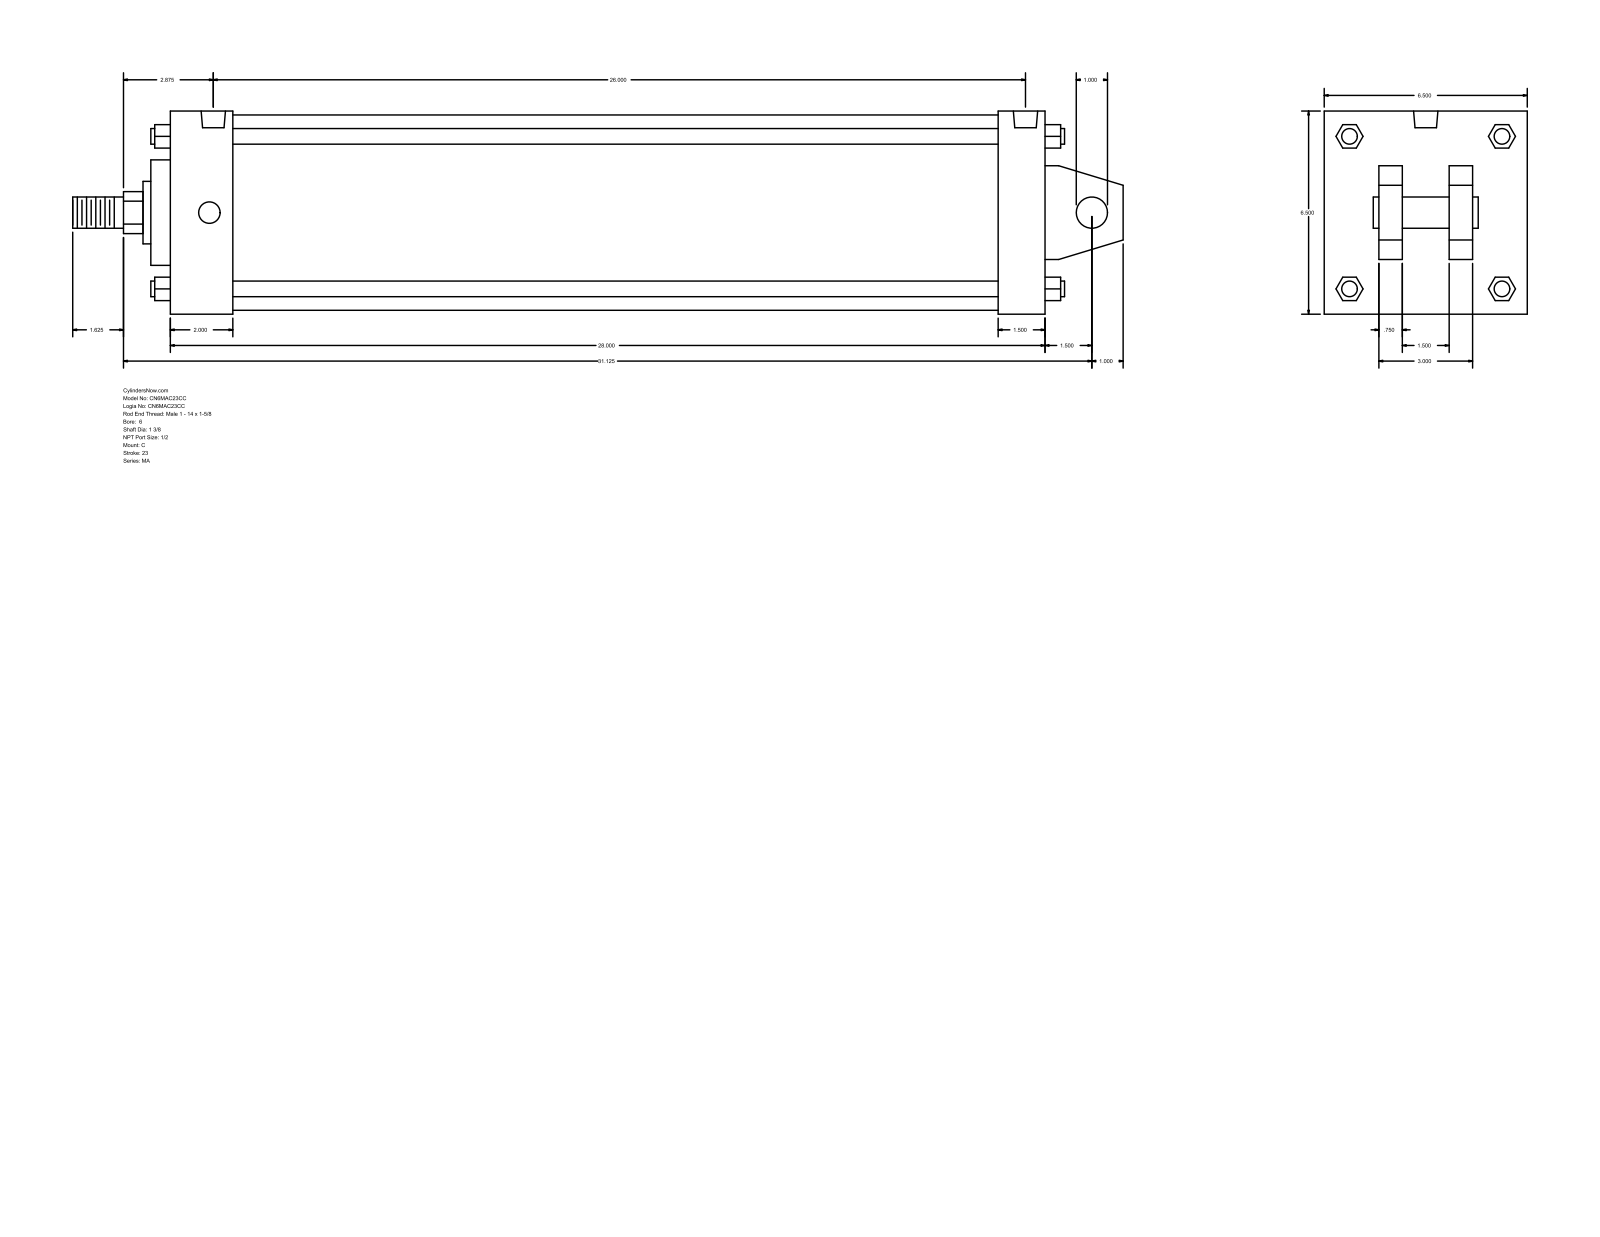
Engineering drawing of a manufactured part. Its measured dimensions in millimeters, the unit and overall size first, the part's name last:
Units: millimetres
Overall size (bounding box): 854.08 × 165.1 × 165.1
Round holes (diameter × count): ⌀17.46 ×4, ⌀19.77 ×2
Round bosses / shafts (diameter × count): ⌀12.7 ×4, ⌀25.4 ×2, ⌀158.75 ×1, ⌀85.72 ×1, ⌀50.8 ×1, ⌀34.92 ×1
Partial cylindrical surfaces — rounded edges, fillets, slot ends (radius × count): R17.06 ×1
Main face-to-face distances: 165.1, 711.2, 38.1, 19.05, 63.5, 101.6, 50.8, 44.45, 120.65, 673.1
Hole centre spacings: 660.4, 3.17, 3.18, 657.22, 660.39, 663.57
Bodies: 0 solids, 141 faces (109 planar, 32 cylindrical, 0 other)
Part name (STEP PRODUCT): MA_C__0600_1.375
STEP written by: GSSL Pune (CONFIG_CONTROL_DESIGN)
